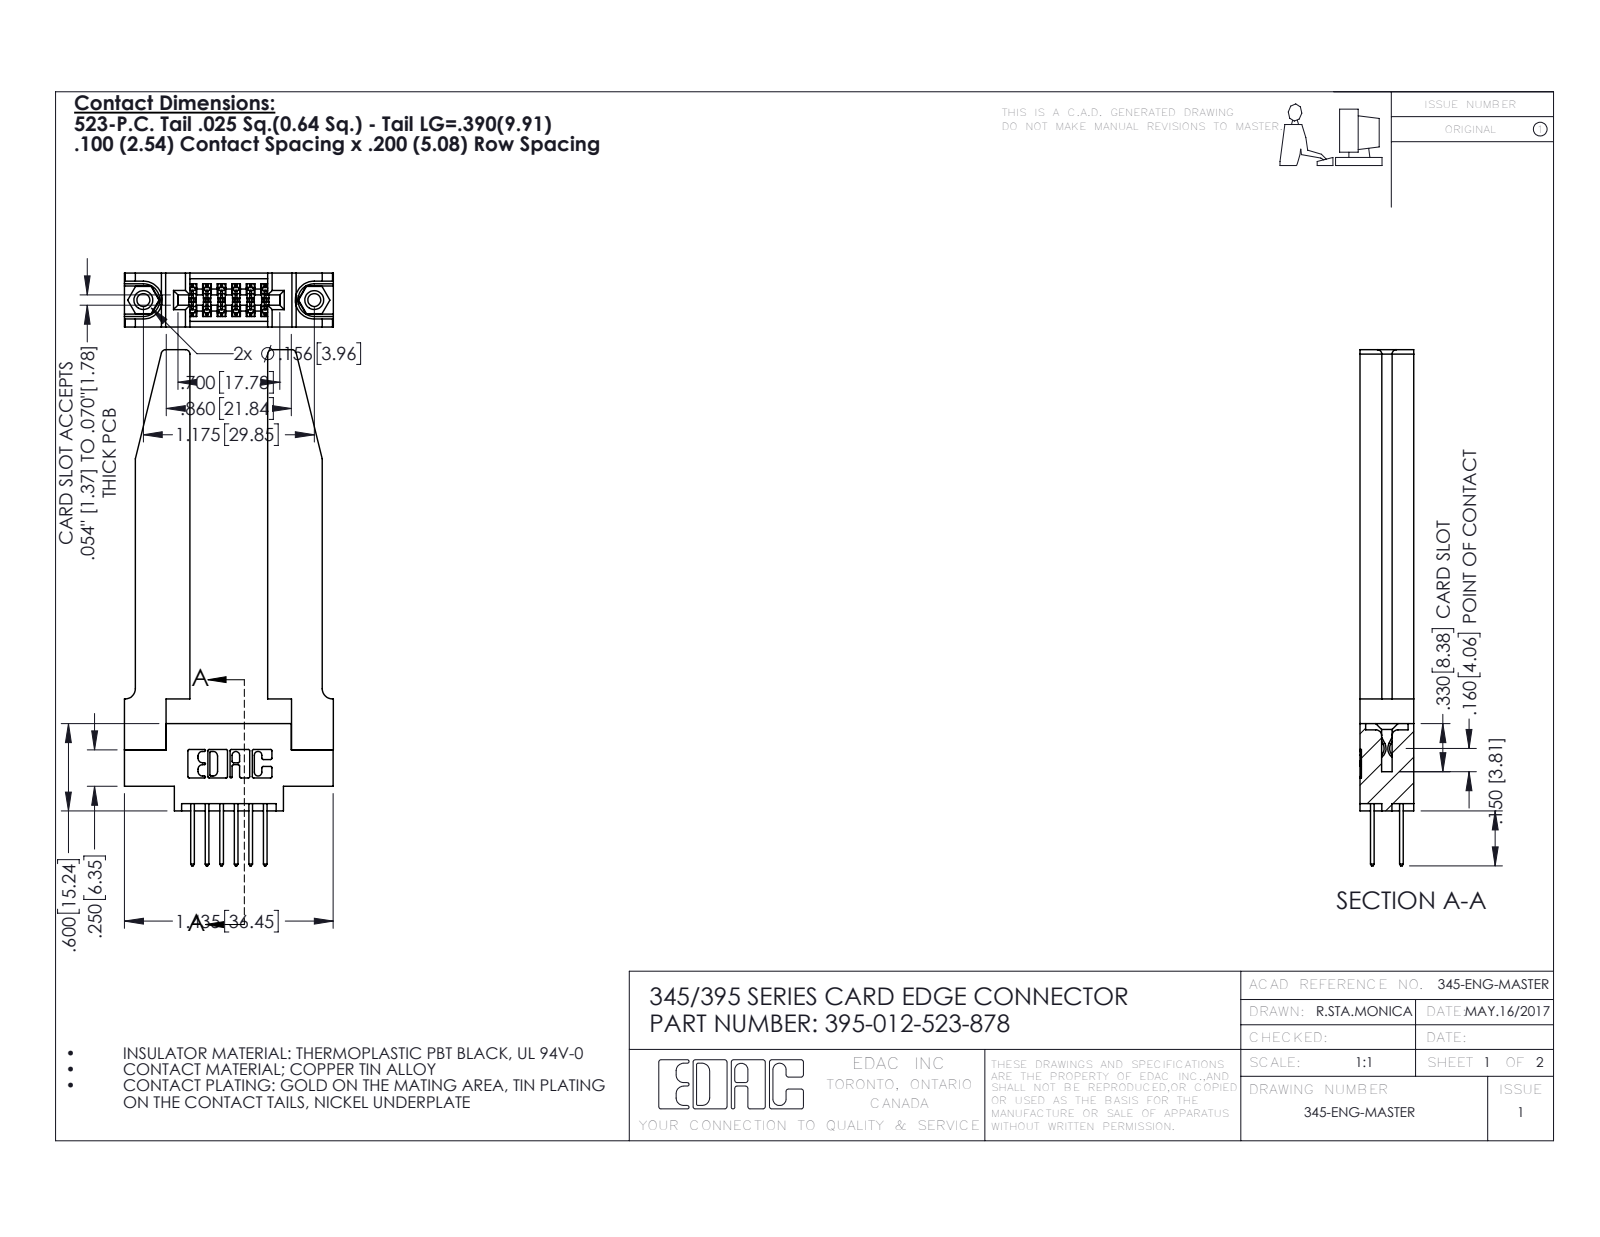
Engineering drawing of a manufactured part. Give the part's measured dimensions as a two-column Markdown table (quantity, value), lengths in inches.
| quantity | value |
| --- | --- |
| part name | 395-012-523-878; 345-220-078_345-220-078; 345 Part_0.170 Offset - 0.156 Dia-TH; 345-250-001_345-250-001-102 (+1 more) |
| STEP written by | SolidWorks 2016 (CONFIG_CONTROL_DESIGN) |
| units | inches |
| bodies | 17 solids, 964 faces (622 planar, 290 cylindrical, 52 other) |
| overall size | 3.547 × 1.436 × 0.37 |
| volume | 0.665 in³ |
| surface area | 17.06 in² |
| round holes (diameter × count) | 0.089 × 2, 0.125 × 2, 0.156 × 2, 0.064 × 1 |
| round bosses / shafts (diameter × count) | 0.155 × 2 |
| partial cylindrical surfaces (radius × count) | 0.01 × 22, 0.006 × 18, 0.01 × 12, 0.03 × 8, 0.007 × 6, 0.031 × 6, 0.026 × 3, 0.014 × 2 |
| main face-to-face distances | 0.37, 0.15, 0.072, 0.148, 0.22, 0.298, 0.077, 0.535, 0.095, 0.2 |
| hole center spacings | 0.27, 0.946, 1.175 |
